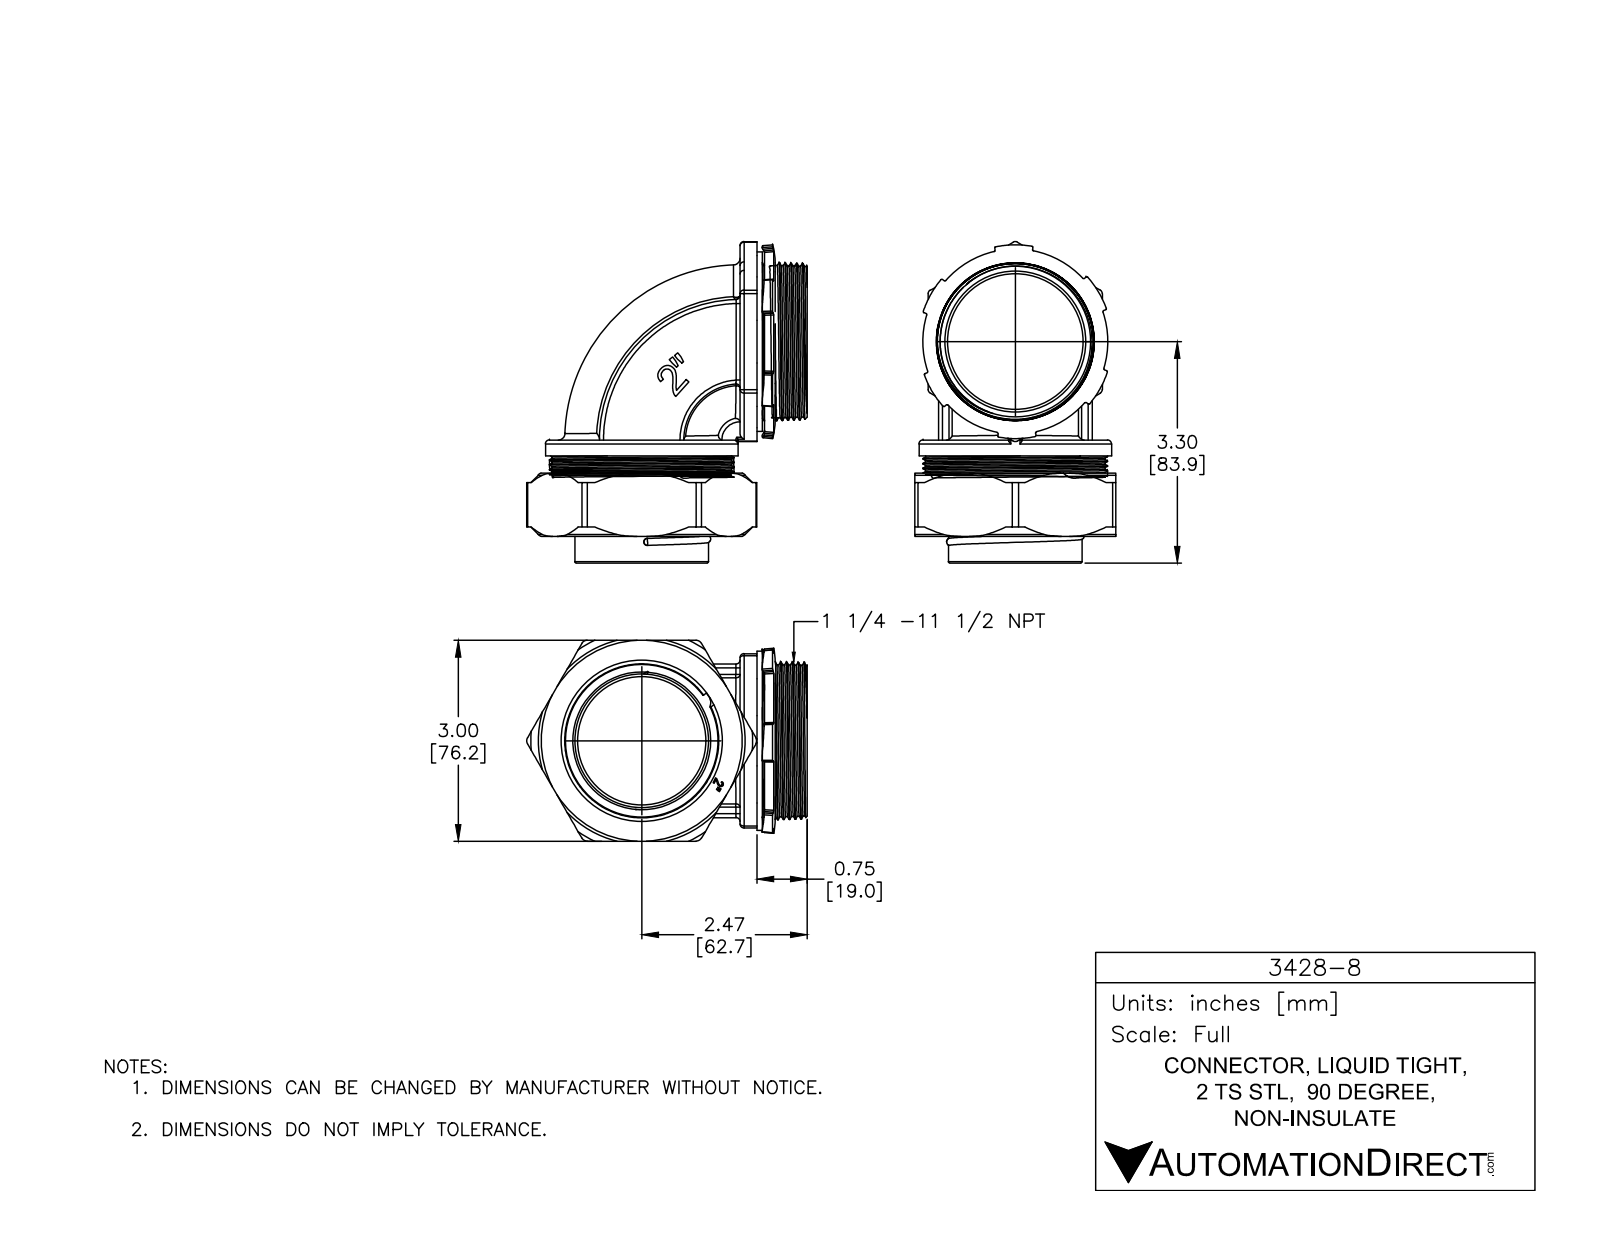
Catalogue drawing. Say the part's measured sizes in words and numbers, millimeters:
The part is named "3428 90DEG BODY; 3408 LOCK NUT; 3428-8; 3408 SEAL_2 (+3 more)". Its 3-D file was written by "SolidWorks 2014 (AUTOMOTIVE_DESIGN)". It is 6 solids with 619 faces: 224 planar, 144 cylindrical and 251 other. Overall it measures 121.8 by 106.3 by 76.2 millimeters. Its volume is 127 400 cubic millimeters and its surface area 97 940 square millimeters. Round holes: 1 of diameter 5.6, 1 of diameter 48.6, 1 of diameter 49.7, 1 of diameter 51.4, 1 of diameter 52.8, 1 of diameter 57.6, 1 of diameter 60, 1 of diameter 61, 1 of diameter 61.2, 1 of diameter 62.8, 1 of diameter 68.6. Round bosses or shafts: 1 of diameter 73, 1 of diameter 69.9, 1 of diameter 68, 1 of diameter 66, 1 of diameter 62, 1 of diameter 50.7, 1 of diameter 49.7, 1 of diameter 4.6. Partial cylindrical surfaces (rounded edges, fillets, slot ends): 16 of radius 1.5, 8 of radius 0.4, 6 of radius 2.4, 4 of radius 0.8, 3 of radius 0.1, 2 of radius 0.1, 2 of radius 1.3, 1 of radius 0.2. The main face-to-face distances are 76.2, 58.3, 30.5, 9, 76.2, 67.3, 67.2, 8.9, 2, 36.6. The hole center spacings are 34.3.
